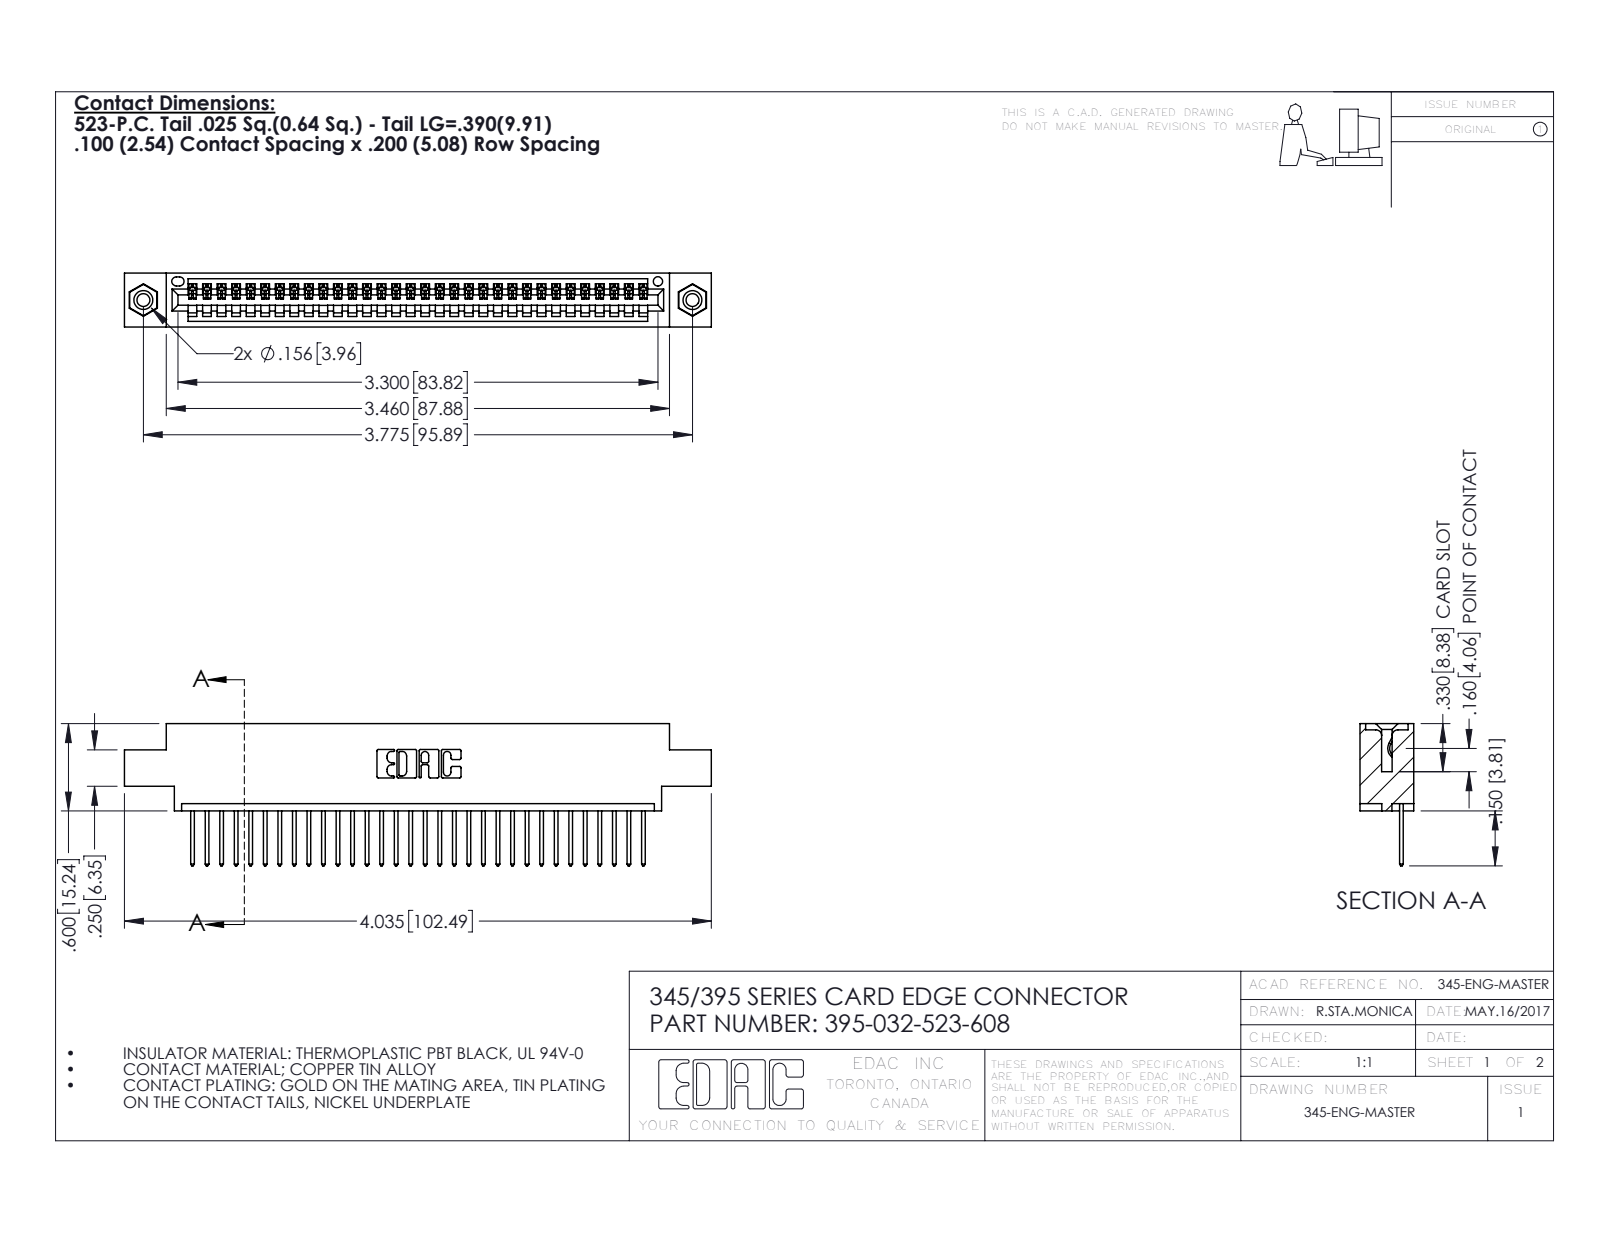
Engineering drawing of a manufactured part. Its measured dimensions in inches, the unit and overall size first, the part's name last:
Units: inches
Overall size (bounding box): 4.035 × 0.977 × 0.37
Round holes (diameter × count): ⌀0.089 ×2, ⌀0.125 ×2, ⌀0.156 ×2, ⌀0.064 ×1
Round bosses / shafts (diameter × count): ⌀0.155 ×2
Partial cylindrical surfaces — rounded edges, fillets, slot ends (radius × count): R0.006 ×64, R0.01 ×64, R0.01 ×22, R0.007 ×6, R0.031 ×6, R0.026 ×3, R0.031 ×2, R0.04 ×2
Main face-to-face distances: 0.072, 0.298, 0.37, 0.2, 0.098, 0.272, 0.025, 0.225, 0.175, 0.149
Hole centre spacings: 0.27, 3.54, 3.775
Volume: 0.581 in³ · Surface area: 19.68 in²
Bodies: 35 solids, 2046 faces (1396 planar, 634 cylindrical, 16 other)
Part name (STEP PRODUCT): 395-032-523-608; 345 Part_0.170 Offset - 0.156 Dia-TI; 345-292-001_345-293-123; 345-250-001_345-250-003-102
STEP written by: SolidWorks 2016 (CONFIG_CONTROL_DESIGN)
